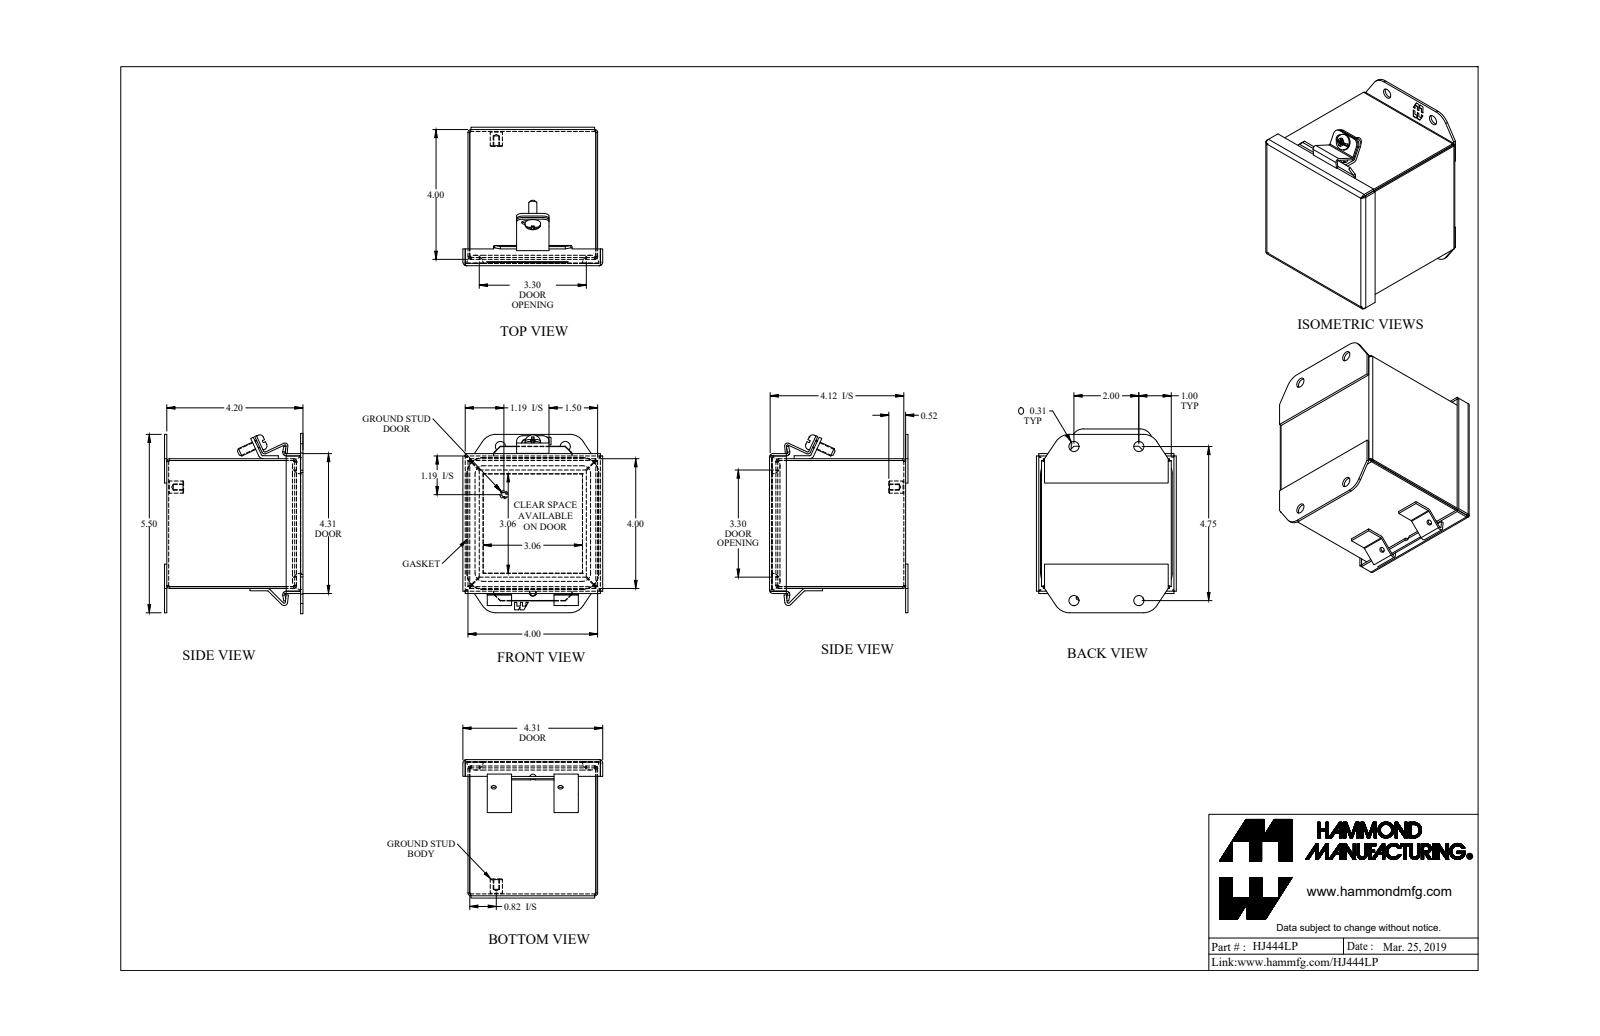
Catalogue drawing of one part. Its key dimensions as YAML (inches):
part_name: "HJ444LP"
step_written_by: "SolidWorks 2018 (AUTOMOTIVE_DESIGN)"
units: inches
bodies: {solids: 12, faces: 470, planar: 274, cylindrical: 120, other: 76}
overall_size: [5.5, 4.312, 4.269]
volume: 9.083
surface_area: 287.1
round_holes:
  - {diameter: 0.313, count: 4}
  - {diameter: 0.156, count: 2}
  - {diameter: 0.156, count: 1}
  - {diameter: 0.213, count: 1}
round_bosses_or_shafts:
  - {diameter: 0.25, count: 2}
  - {diameter: 0.48, count: 1}
  - {diameter: 0.375, count: 1}
  - {diameter: 0.188, count: 1}
partial_cylinders:
  - {radius: 0.188, count: 14}
  - {radius: 0.029, count: 10}
  - {radius: 0.086, count: 10}
  - {radius: 0.036, count: 8}
  - {radius: 0.108, count: 8}
  - {radius: 0.25, count: 4}
  - {radius: 0.499, count: 4}
  - {radius: 0.5, count: 4}
face_to_face_distances: [0.057, 3.943, 0.072, 4, 3.886, 4.197, 4.125, 0.057, 4.068, 4.14]
hole_center_spacings: [2, 4.75, 5.154, 1.257, 2.06, 2.466, 3.502, 4.094]
